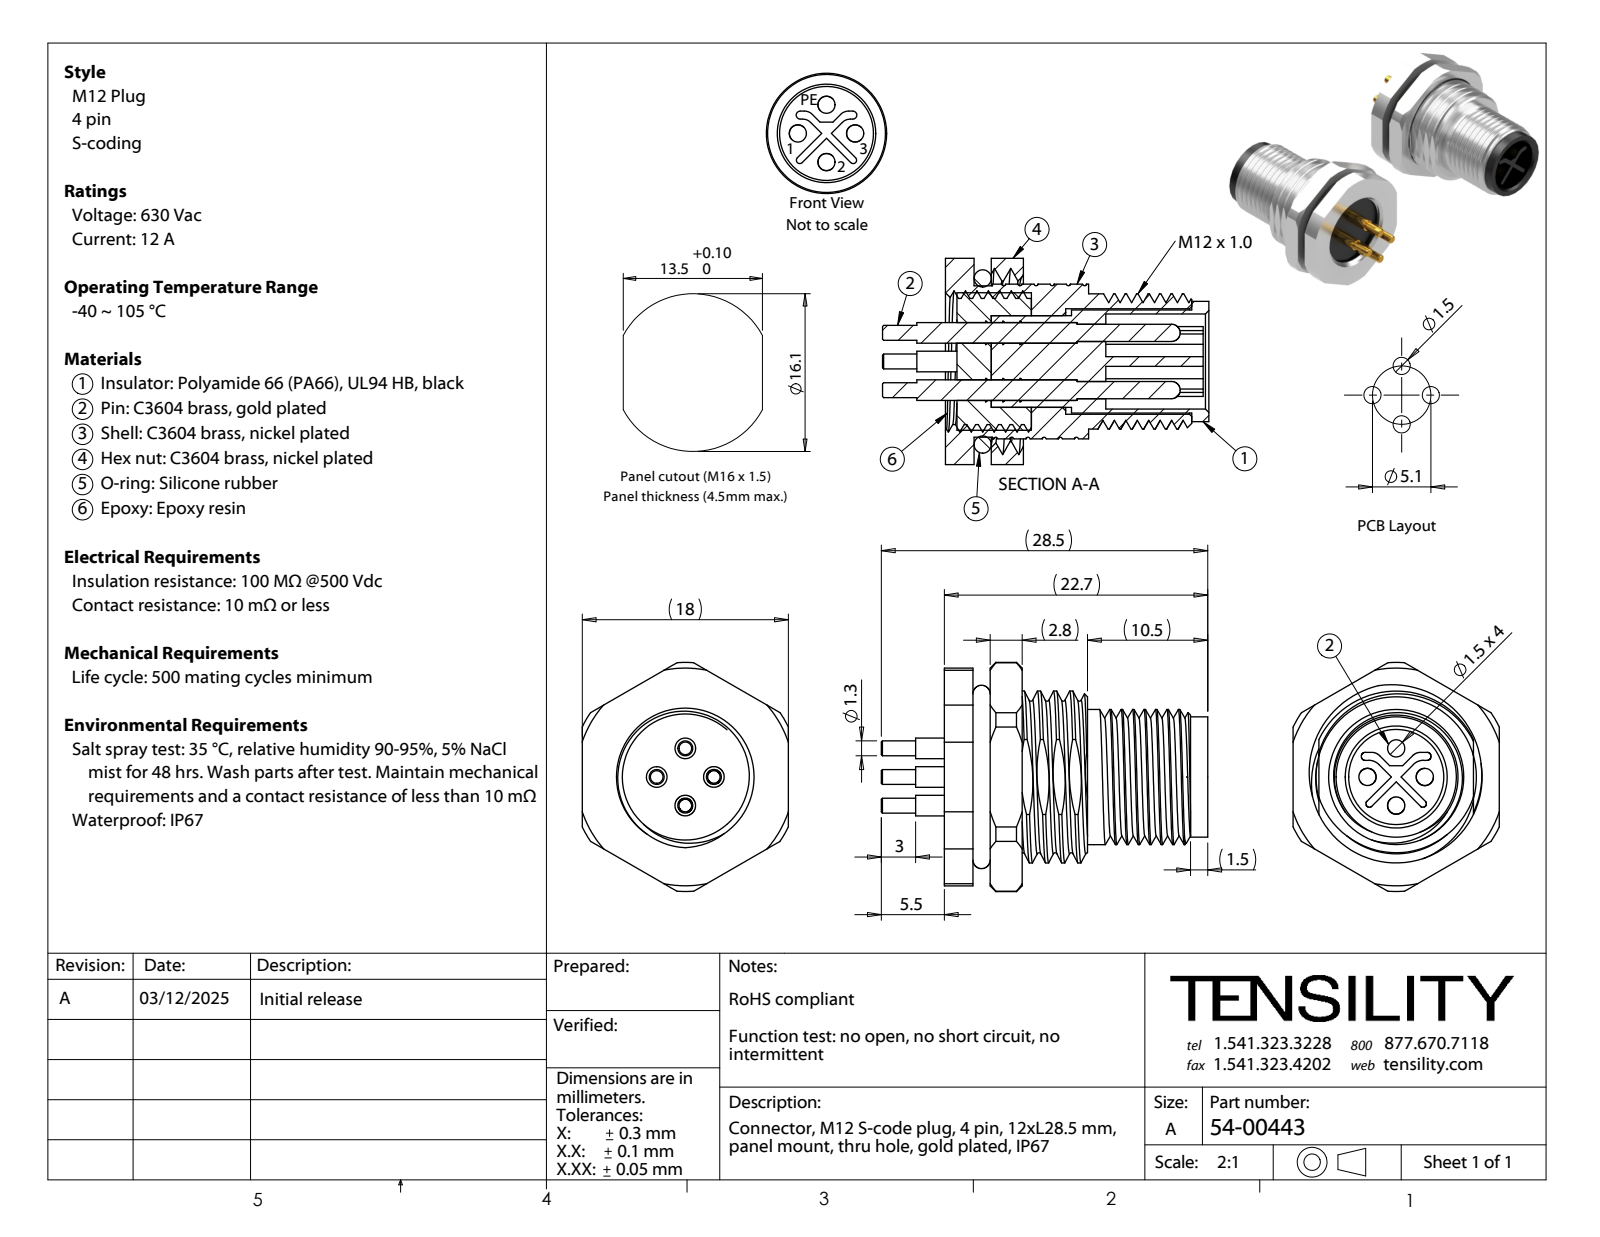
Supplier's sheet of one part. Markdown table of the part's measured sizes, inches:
| quantity | value |
| --- | --- |
| part name | 54-00443-03L; 54-00443-04; 54-00443-03; 54-00443-01 (+3 more) |
| STEP written by | SolidWorks 2021 (CONFIG_CONTROL_DESIGN) |
| units | inches |
| bodies | 9 solids, 342 faces (88 planar, 158 cylindrical, 96 other) |
| overall size | 1.122 × 0.787 × 0.709 |
| volume | 0.193 in³ |
| surface area | 9.329 in² |
| round holes (diameter × count) | 0.059 × 4, 0.315 × 1, 0.327 × 1, 0.362 × 1, 0.433 × 1, 0.551 × 1 |
| round bosses / shafts (diameter × count) | 0.071 × 4, 0.051 × 4, 0.52 × 1, 0.472 × 1, 0.465 × 1, 0.413 × 1, 0.354 × 1 |
| partial cylindrical surfaces (radius × count) | 0.012 × 2, 0.014 × 2, 0.039 × 2, 0.05 × 2, 0.295 × 1, 0.374 × 1, 0.394 × 1 |
| main face-to-face distances | 0.059, 0.157, 0.295, 0.256, 0.197, 0.098, 0.138, 0.118, 0.039, 0.709 |
| hole center spacings | 0.098, 0.139, 0.197 |
